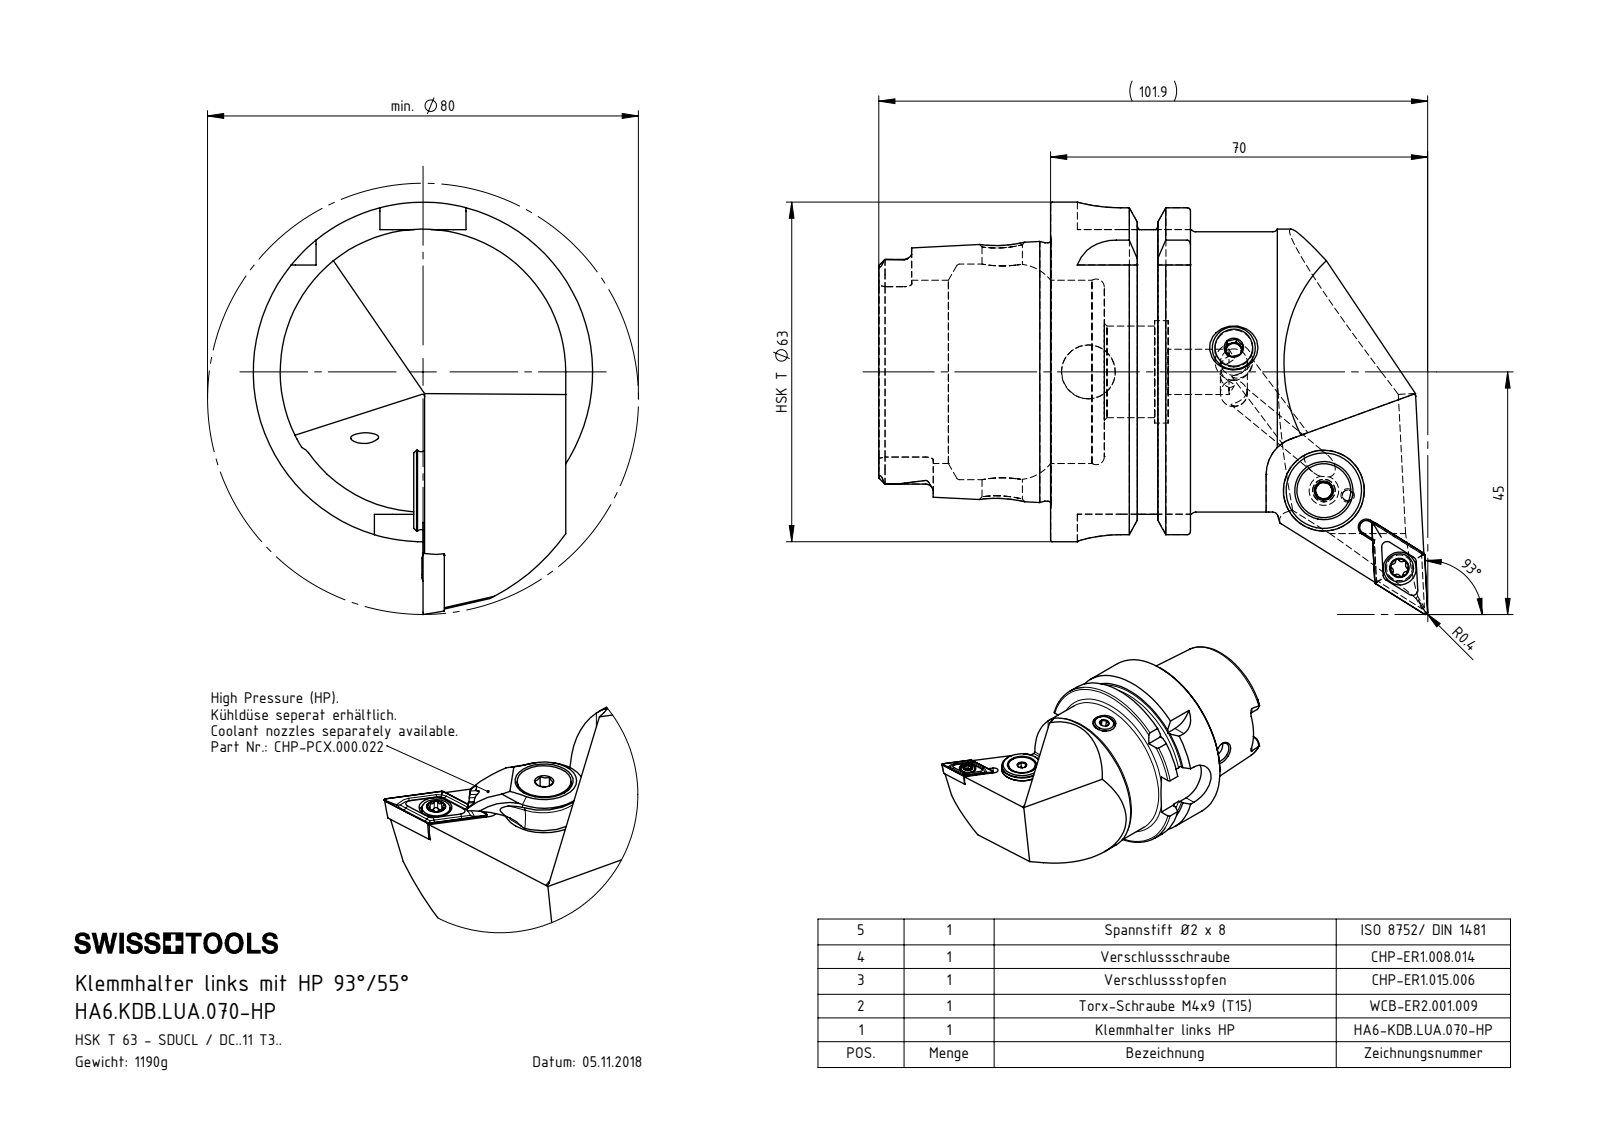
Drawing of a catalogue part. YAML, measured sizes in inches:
part_name: "WCB-ER2.001.009_A; DIN 7991 - M5x15; DIN 3771 - 13x1; CHP-ER1.015.006_A (+6 more)"
step_written_by: "SolidWorks 2017 (AUTOMOTIVE_DESIGN)"
units: inches
bodies: {solids: 8, faces: 416, planar: 118, cylindrical: 120, other: 178}
overall_size: [4.012, 3.012, 2.48]
volume: 9.182
surface_area: 51.54
round_holes:
  - {diameter: 0.165, count: 2}
  - {diameter: 0.197, count: 2}
  - {diameter: 0.047, count: 1}
  - {diameter: 0.079, count: 1}
  - {diameter: 0.098, count: 1}
  - {diameter: 0.118, count: 1}
  - {diameter: 0.13, count: 1}
  - {diameter: 0.173, count: 1}
  - {diameter: 0.205, count: 1}
  - {diameter: 0.24, count: 1}
  - {diameter: 0.276, count: 1}
  - {diameter: 0.295, count: 1}
round_bosses_or_shafts:
  - {diameter: 2.48, count: 1}
  - {diameter: 2.163, count: 1}
  - {diameter: 2.047, count: 1}
  - {diameter: 1.887, count: 1}
  - {diameter: 0.591, count: 1}
  - {diameter: 0.528, count: 1}
  - {diameter: 0.394, count: 1}
  - {diameter: 0.315, count: 1}
partial_cylinders:
  - {radius: 0.013, count: 6}
  - {radius: 0.023, count: 6}
  - {radius: 0.055, count: 6}
  - {radius: 0.315, count: 4}
  - {radius: 0.02, count: 2}
  - {radius: 0.111, count: 2}
  - {radius: 0.113, count: 2}
  - {radius: 0.276, count: 2}
face_to_face_distances: [1.022, 0.63, 0.392, 1.031, 1.256, 1.648, 2.278, 2.079, 0.858, 0.467]
hole_center_spacings: [0.177, 0.65, 0.655, 0.789, 0.794, 1.927, 2.099, 2.686]
